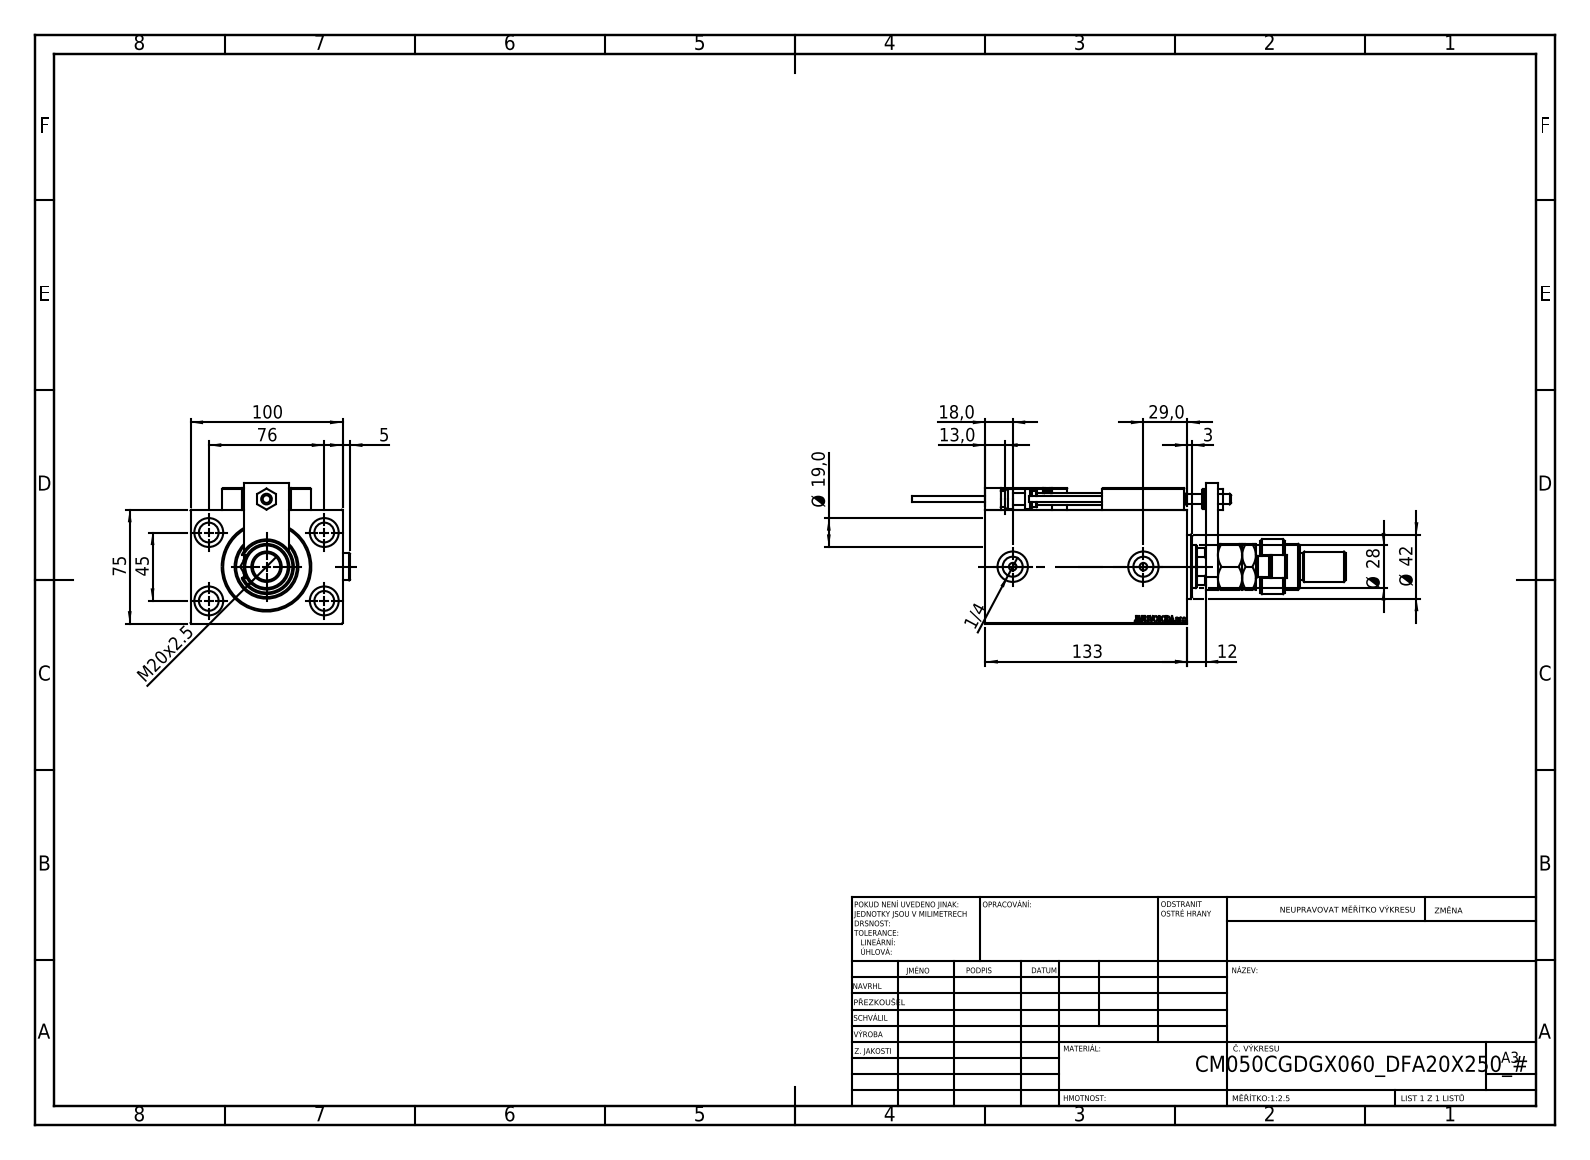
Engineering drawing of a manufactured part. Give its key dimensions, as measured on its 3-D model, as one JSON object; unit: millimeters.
{"part_name": "ZARAZKA; SWITCH_X_FRONT_BACK; ALLEN BOLT D5; Zatka_OIL_PORT (+8 more)", "step_written_by": "SolidWorks 2019 (CONFIG_CONTROL_DESIGN)", "units": "millimeters", "bodies": {"solids": 27, "faces": 1424, "planar": 623, "cylindrical": 219, "other": 582}, "overall_size": [285, 104.9, 92.5], "volume_mm3": 932093, "surface_area_mm2": 175855, "round_holes": [[8, 5], [3.2, 4], [4, 4], [5, 4], [13, 4], [19, 4], [20, 3], [13.16, 2], [7, 1], [18.5, 1], [28, 1], [31.5, 1]], "round_bosses_or_shafts": [[18, 3], [5, 2], [3.8, 2], [42, 1], [36, 1], [30, 1], [22, 1], [14, 1]], "partial_cylinders_radius": [[0.3, 30], [3, 2], [7.5, 1], [12, 1], [13.5, 1]], "face_to_face_distances": [75, 100, 14, 133, 12, 119, 20, 8, 24, 25], "hole_center_spacings": [44.16, 11.37, 20, 29.59, 29.69, 36.06, 42.19, 43.91]}
